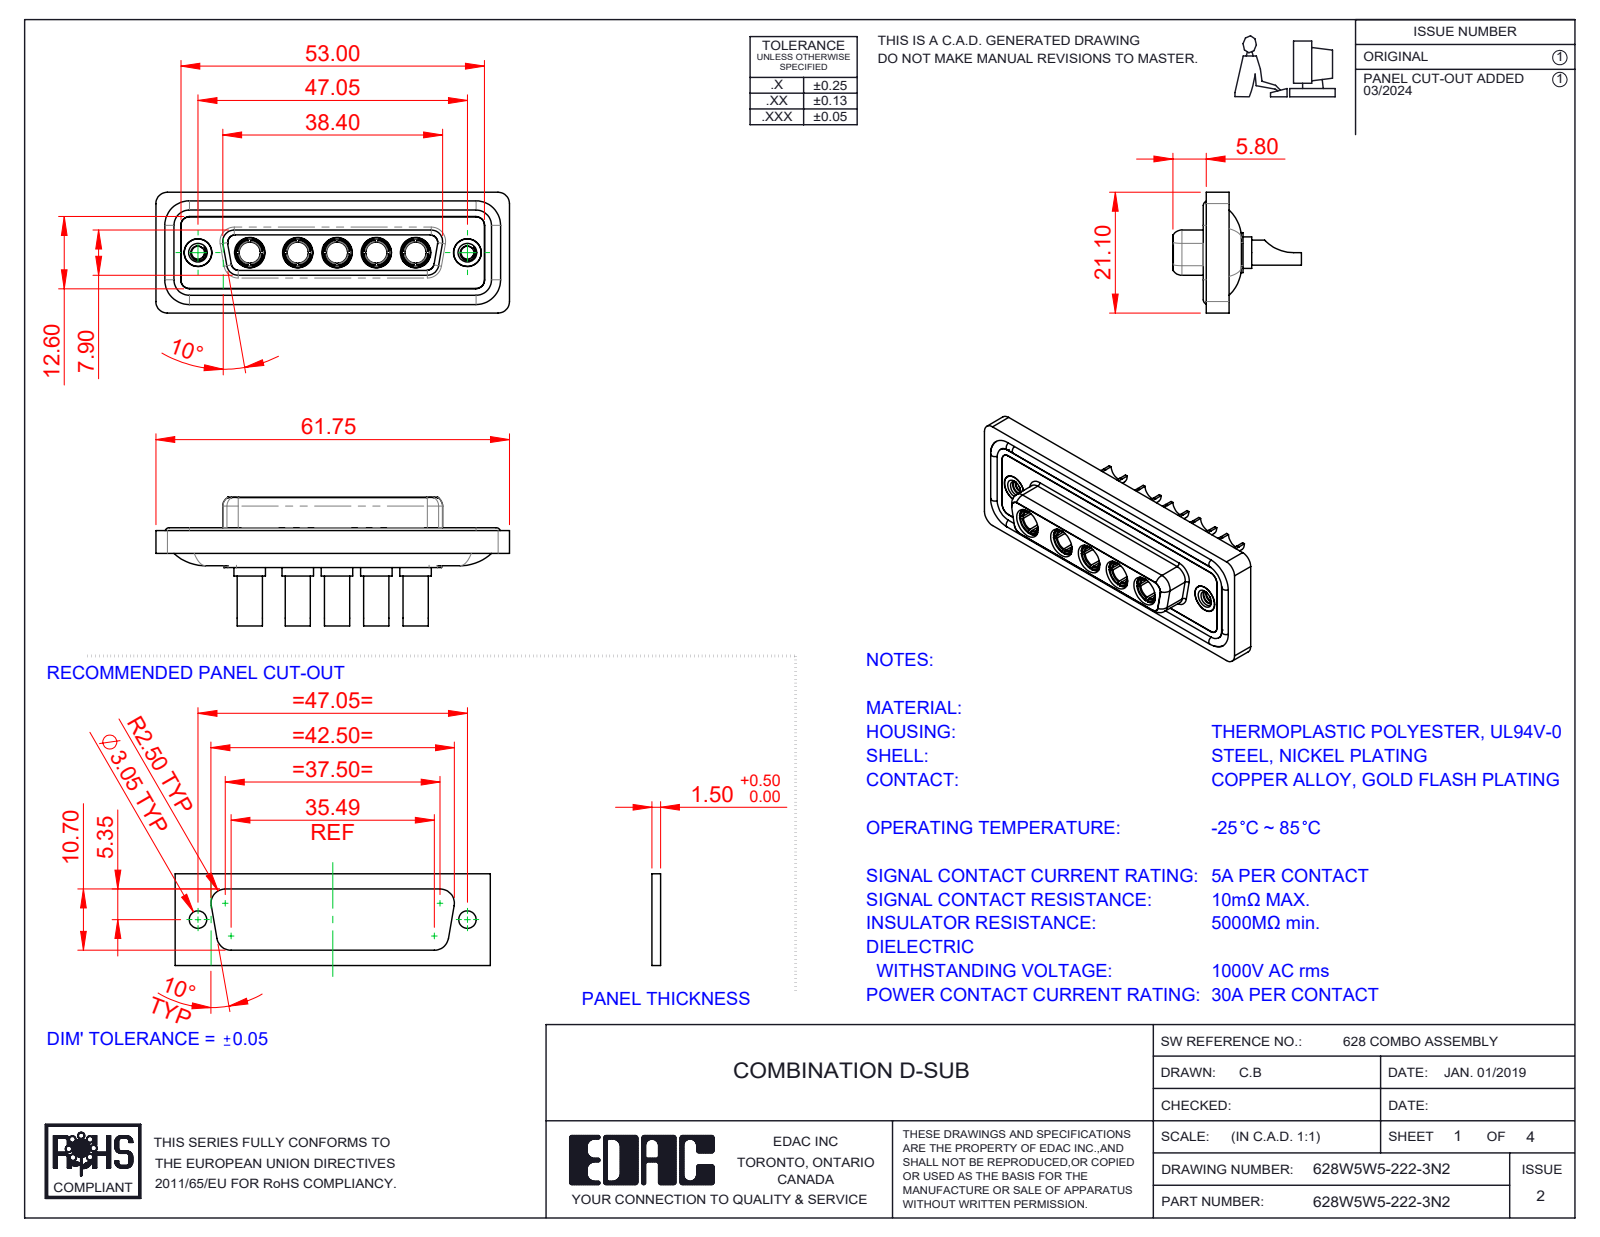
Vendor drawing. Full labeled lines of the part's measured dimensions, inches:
Part name (STEP PRODUCT): Power Socket_30A SC; 628Combo Housing_5W5; 628W5W5-222-3N2; 628Combo Shell Front_25 Contacts (+3 more)
STEP written by: SolidWorks 2023 (CONFIG_CONTROL_DESIGN)
Units: inches
Bodies: 17 solids, 786 faces (265 planar, 318 cylindrical, 203 other)
Overall size (bounding box): 2.431 × 0.884 × 0.831
Volume: 0.506 in³ · Surface area: 21.63 in²
Round holes (diameter × count): ⌀0.191 ×7, ⌀0.138 ×5, ⌀0.146 ×5, ⌀0.209 ×5, ⌀0.089 ×2, ⌀0.157 ×2, ⌀0.159 ×2, ⌀0.197 ×2
Round bosses / shafts (diameter × count): ⌀0.217 ×5, ⌀0.205 ×5, ⌀0.195 ×5, ⌀0.187 ×5, ⌀0.173 ×5, ⌀0.148 ×5, ⌀0.063 ×4, ⌀0.195 ×2
Partial cylindrical surfaces — rounded edges, fillets, slot ends (radius × count): R0.059 ×22, R0.079 ×18, R0.053 ×8, R0.063 ×8, R0.083 ×5, R0.01 ×4, R0.02 ×4, R0.024 ×4
Main face-to-face distances: 0.016, 0.071, 0.293, 0.222, 0.02, 0.278, 0.26, 0.063, 0.043, 0.114
Hole centre spacings: 0.27, 0.356, 0.54, 1.496, 0.33, 0.6, 0.626, 0.686
